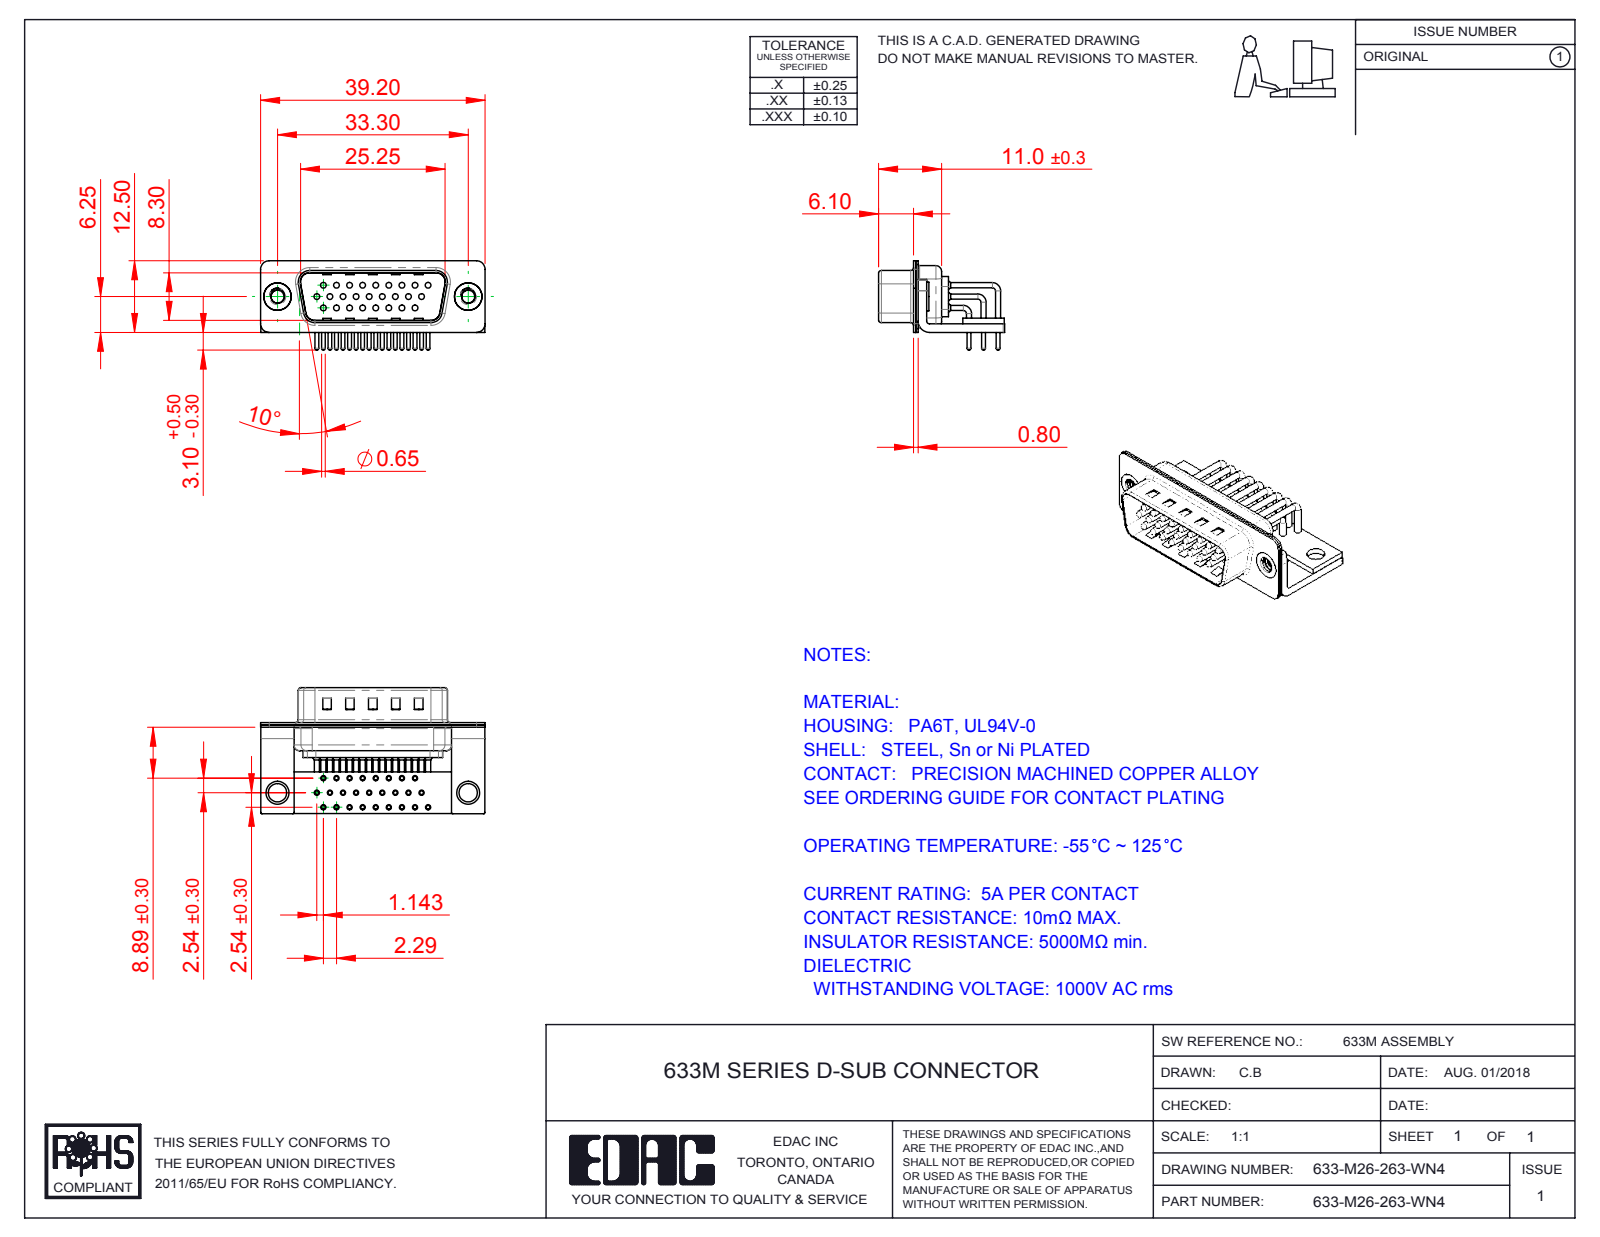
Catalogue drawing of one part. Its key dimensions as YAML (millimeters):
part_name: "633M Stabilizer Board_26 Contacts; 633M Contact Row 2; 633-M26-263-WN4; 633M Contact Row 3 (+6 more)"
step_written_by: "SolidWorks 2016 (CONFIG_CONTROL_DESIGN)"
units: millimeters
bodies: {solids: 34, faces: 3302, planar: 1829, cylindrical: 1143, other: 330}
overall_size: [39.2, 22, 15.6]
volume: 2620
surface_area: 7989
round_holes:
  - {diameter: 0.9, count: 26}
  - {diameter: 1, count: 26}
  - {diameter: 1.7, count: 26}
  - {diameter: 2, count: 26}
  - {diameter: 2.26, count: 2}
  - {diameter: 3.2, count: 2}
  - {diameter: 4, count: 2}
  - {diameter: 4.8, count: 2}
round_bosses_or_shafts:
  - {diameter: 1.5, count: 26}
  - {diameter: 0.9, count: 26}
  - {diameter: 0.65, count: 26}
  - {diameter: 5, count: 2}
  - {diameter: 4.9, count: 2}
partial_cylinders:
  - {radius: 1.01, count: 26}
  - {radius: 0.25, count: 16}
  - {radius: 1.5, count: 16}
  - {radius: 2, count: 13}
  - {radius: 0.5, count: 9}
  - {radius: 1.6, count: 8}
  - {radius: 0.6, count: 4}
  - {radius: 0.65, count: 4}
face_to_face_distances: [0.4, 1.5, 0.85, 0.8, 1.25, 1, 1.9, 10.4, 9.55, 2.5]
hole_center_spacings: [4.57, 2.29, 2.28, 3.96, 6.86, 4.27, 6.05, 2.78]
